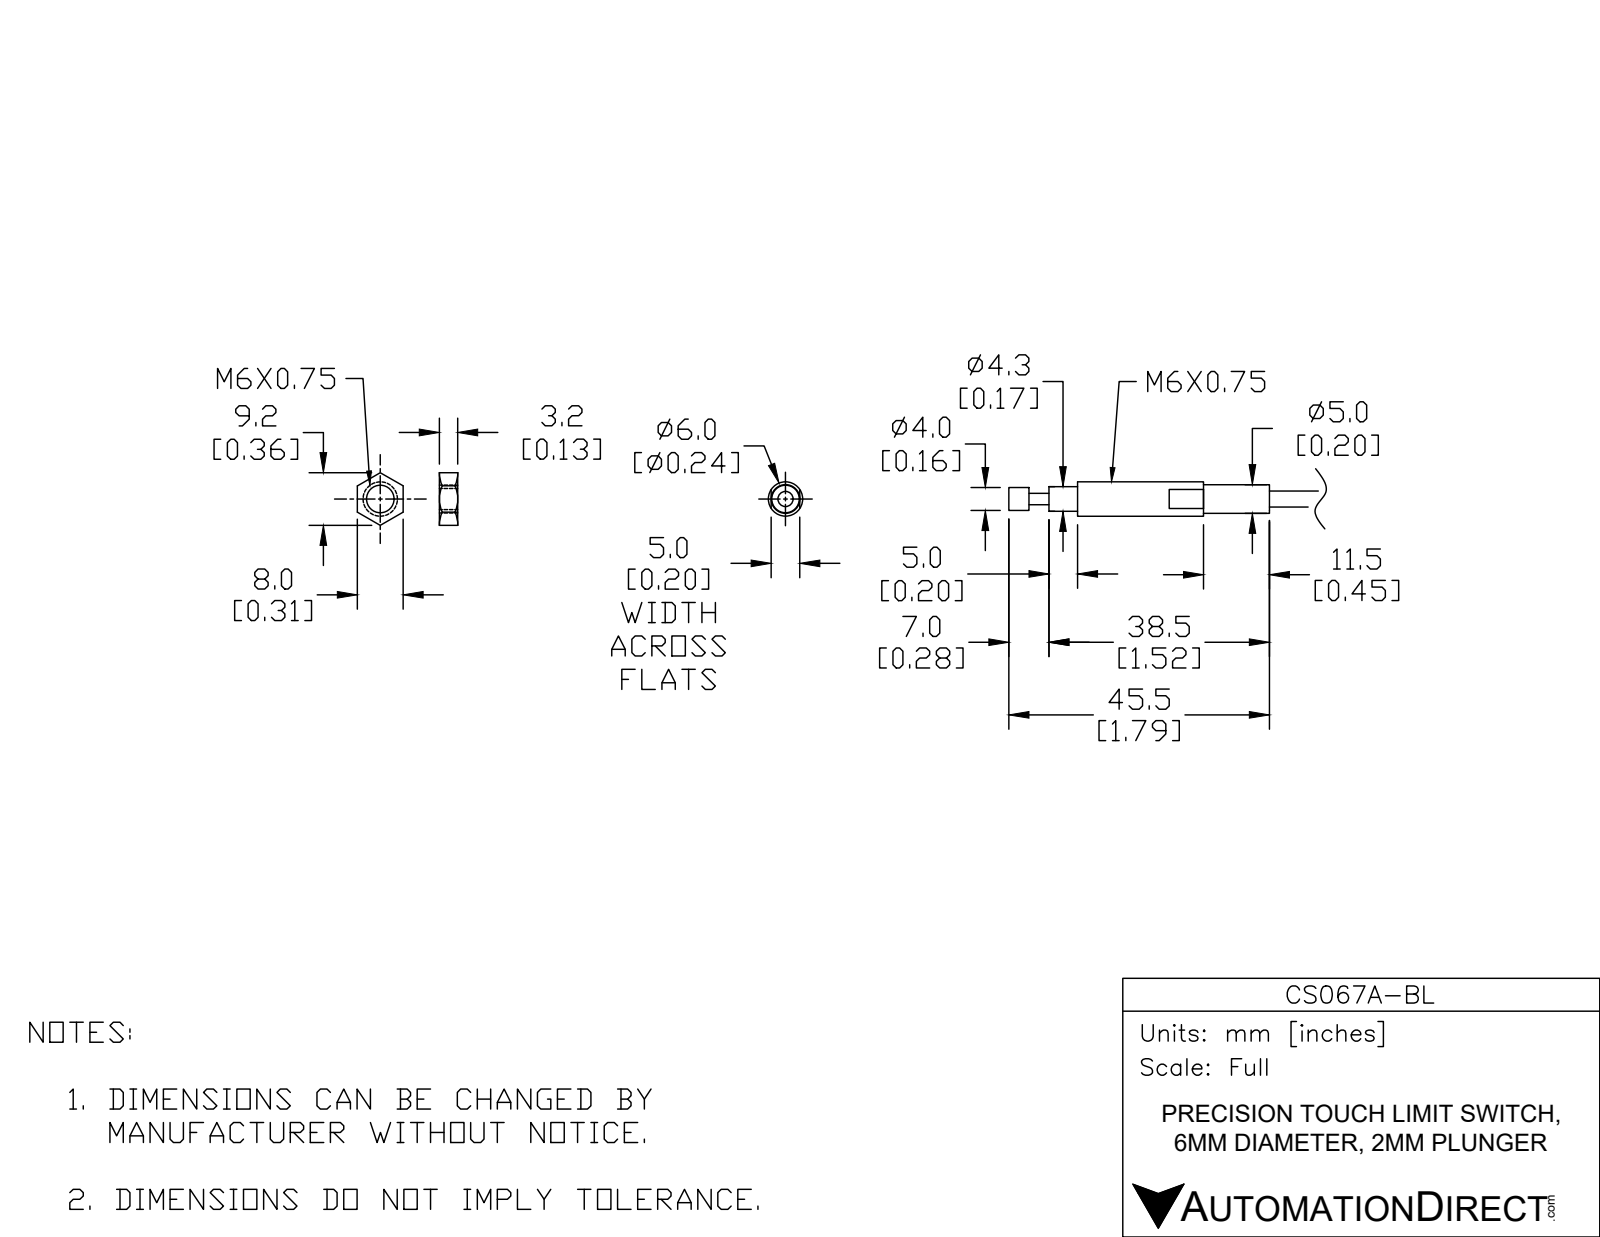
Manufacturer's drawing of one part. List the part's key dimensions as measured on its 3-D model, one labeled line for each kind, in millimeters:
Part name (STEP PRODUCT): CS067A-BL
STEP written by: SolidWorks 2017 (CONFIG_CONTROL_DESIGN)
Units: millimetres
Bodies: 2 solids, 143 faces (16 planar, 76 cylindrical, 51 other)
Overall size (bounding box): 100.56 × 6 × 6
Volume: 1 439 mm³ · Surface area: 1 625 mm²
Round bosses / shafts (diameter × count): ⌀6 ×1, ⌀5 ×1, ⌀4.5 ×1, ⌀4.3 ×1, ⌀4 ×1, ⌀2.8 ×1, ⌀2 ×1
Main face-to-face distances: 5, 3.5, 8.5, 42, 45.5, 7, 38.5, 65.56, 90.56, 58.56
